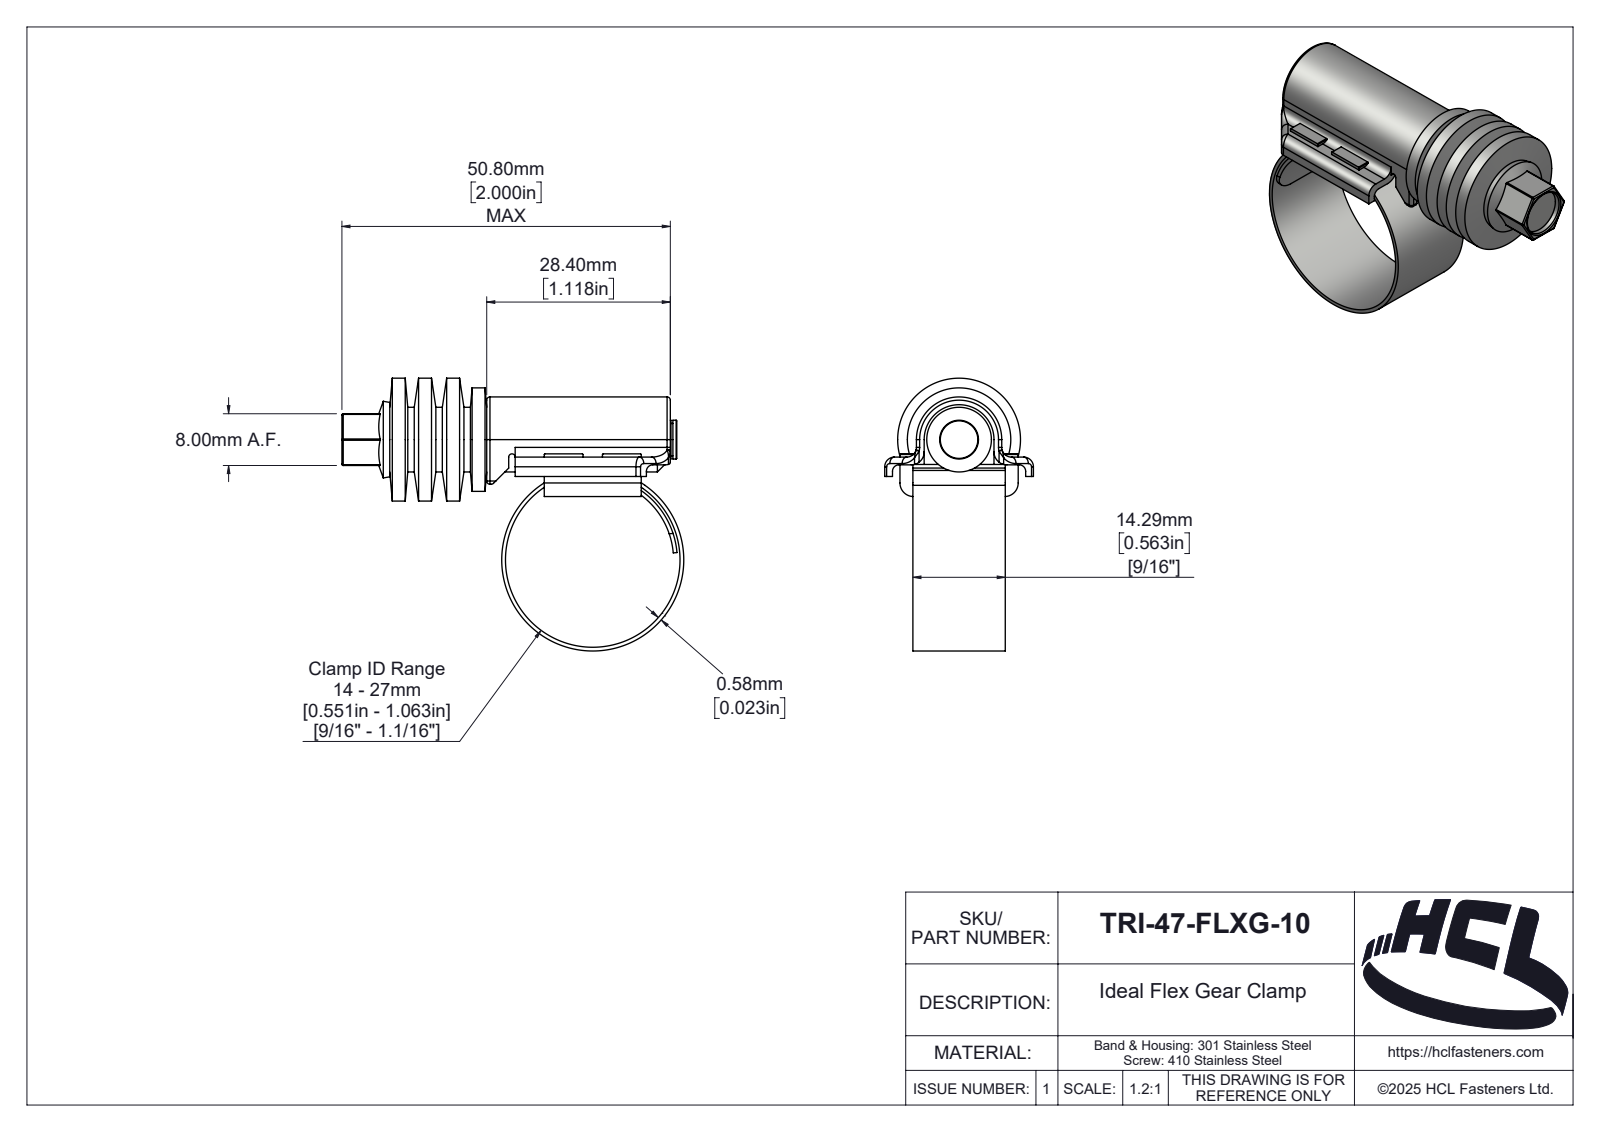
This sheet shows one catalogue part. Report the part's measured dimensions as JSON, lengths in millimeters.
{"part_name": "TRI-47-FLXG-10", "step_written_by": "SolidWorks 2025 (AUTOMOTIVE_DESIGN)", "units": "millimeters", "bodies": {"solids": 4, "faces": 323, "planar": 88, "cylindrical": 139, "other": 96}, "overall_size": [52.88, 42.18, 23], "volume_mm3": 8522, "surface_area_mm2": 9833, "round_holes": [[7, 1], [27, 1]], "round_bosses_or_shafts": [[28.16, 1], [19, 1], [16, 1], [10, 1], [6, 1], [5, 1]], "partial_cylinders_radius": [[0.2, 12], [0.5, 9], [1, 8], [1.5, 4], [3, 4], [2, 3], [0.1, 2], [2.1, 2]], "face_to_face_distances": [2, 1.2, 4.9, 1.74, 12.54, 16.29, 6.1, 0.54, 13.74, 12]}
